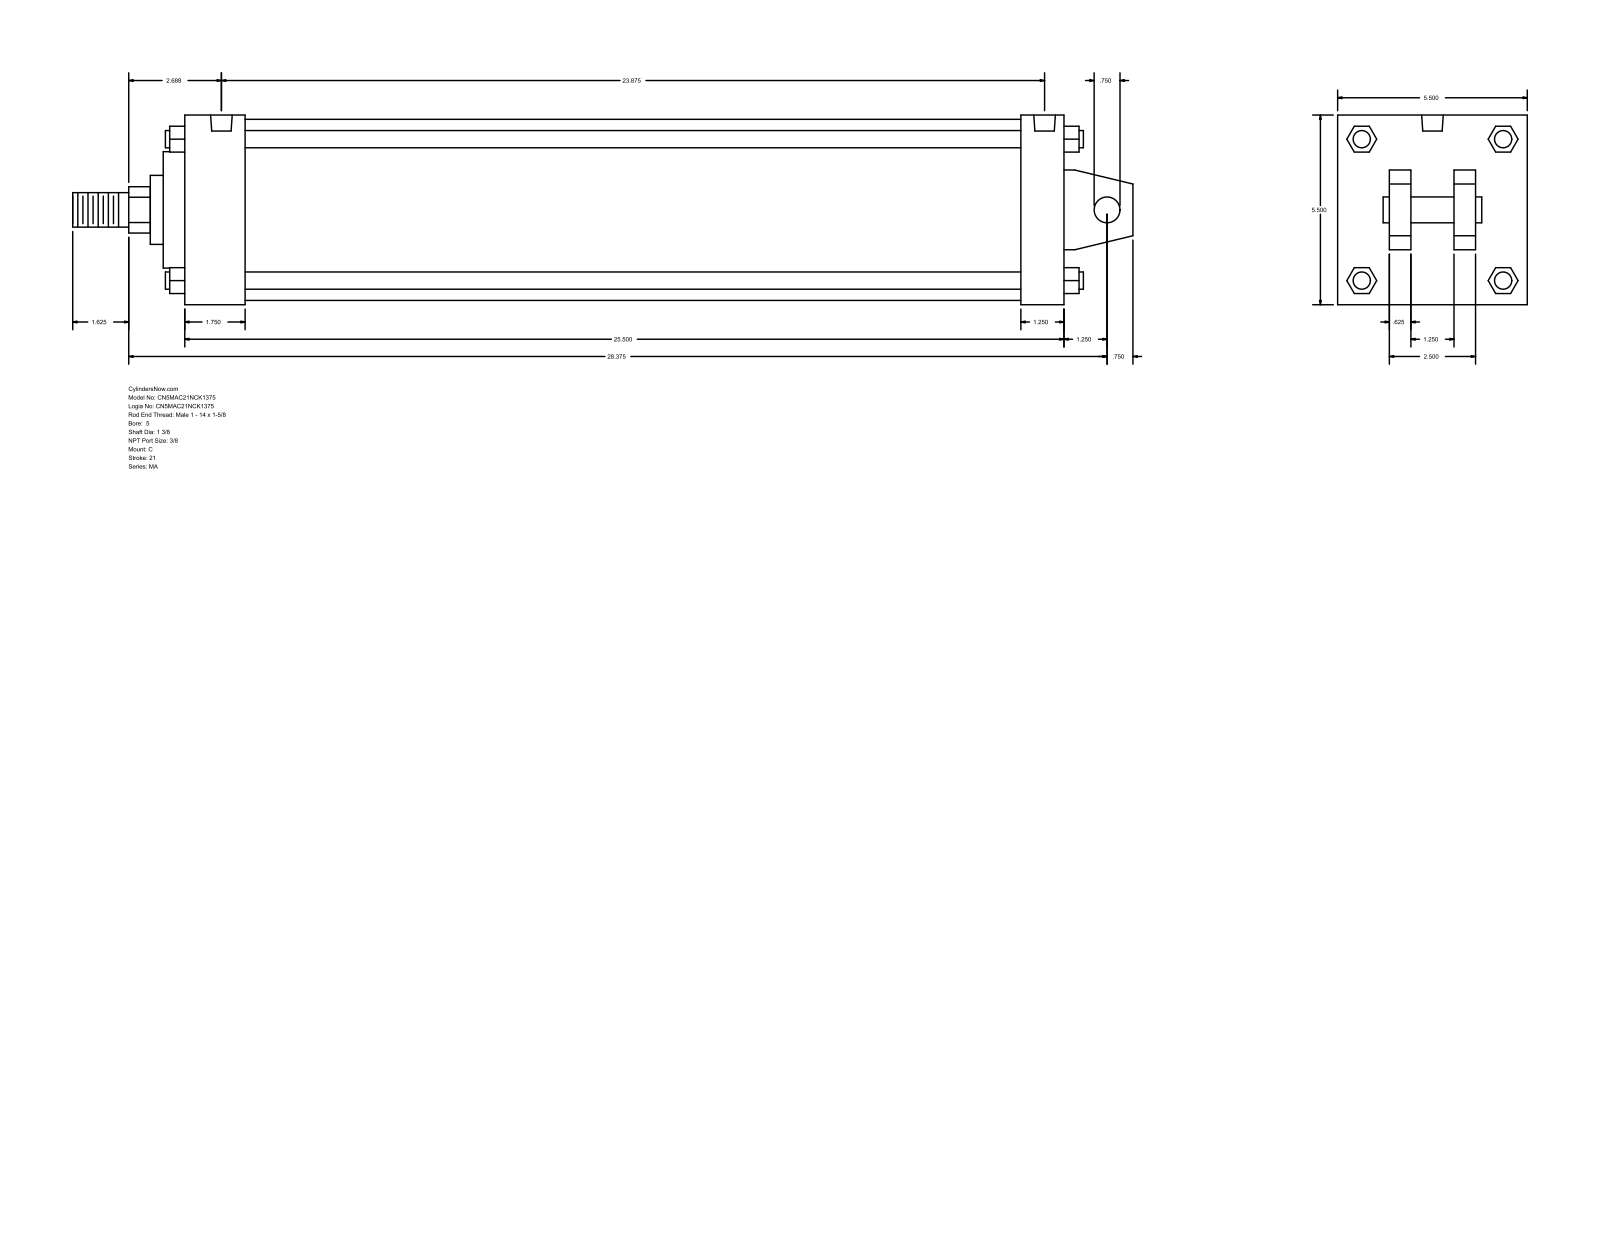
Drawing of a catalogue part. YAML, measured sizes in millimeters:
part_name: "MA_C__0500_1.375"
step_written_by: "GSSL Pune (CONFIG_CONTROL_DESIGN)"
units: millimeters
bodies: {solids: 0, faces: 141, planar: 109, cylindrical: 32, other: 0}
overall_size: [781.05, 139.7, 139.7]
round_holes:
  - {diameter: 11.11, count: 4}
  - {diameter: 15.93, count: 2}
round_bosses_or_shafts:
  - {diameter: 12.7, count: 4}
  - {diameter: 133.35, count: 1}
  - {diameter: 85.72, count: 1}
  - {diameter: 50.8, count: 1}
  - {diameter: 34.92, count: 1}
  - {diameter: 25.4, count: 1}
  - {diameter: 19.05, count: 1}
partial_cylinders:
  - {radius: 17.06, count: 1}
face_to_face_distances: [139.7, 647.71, 15.87, 615.96, 31.75, 44.45, 571.51, 603.26, 53.97, 38.1]
hole_center_spacings: [4.77, 596.89, 601.66, 606.43]
